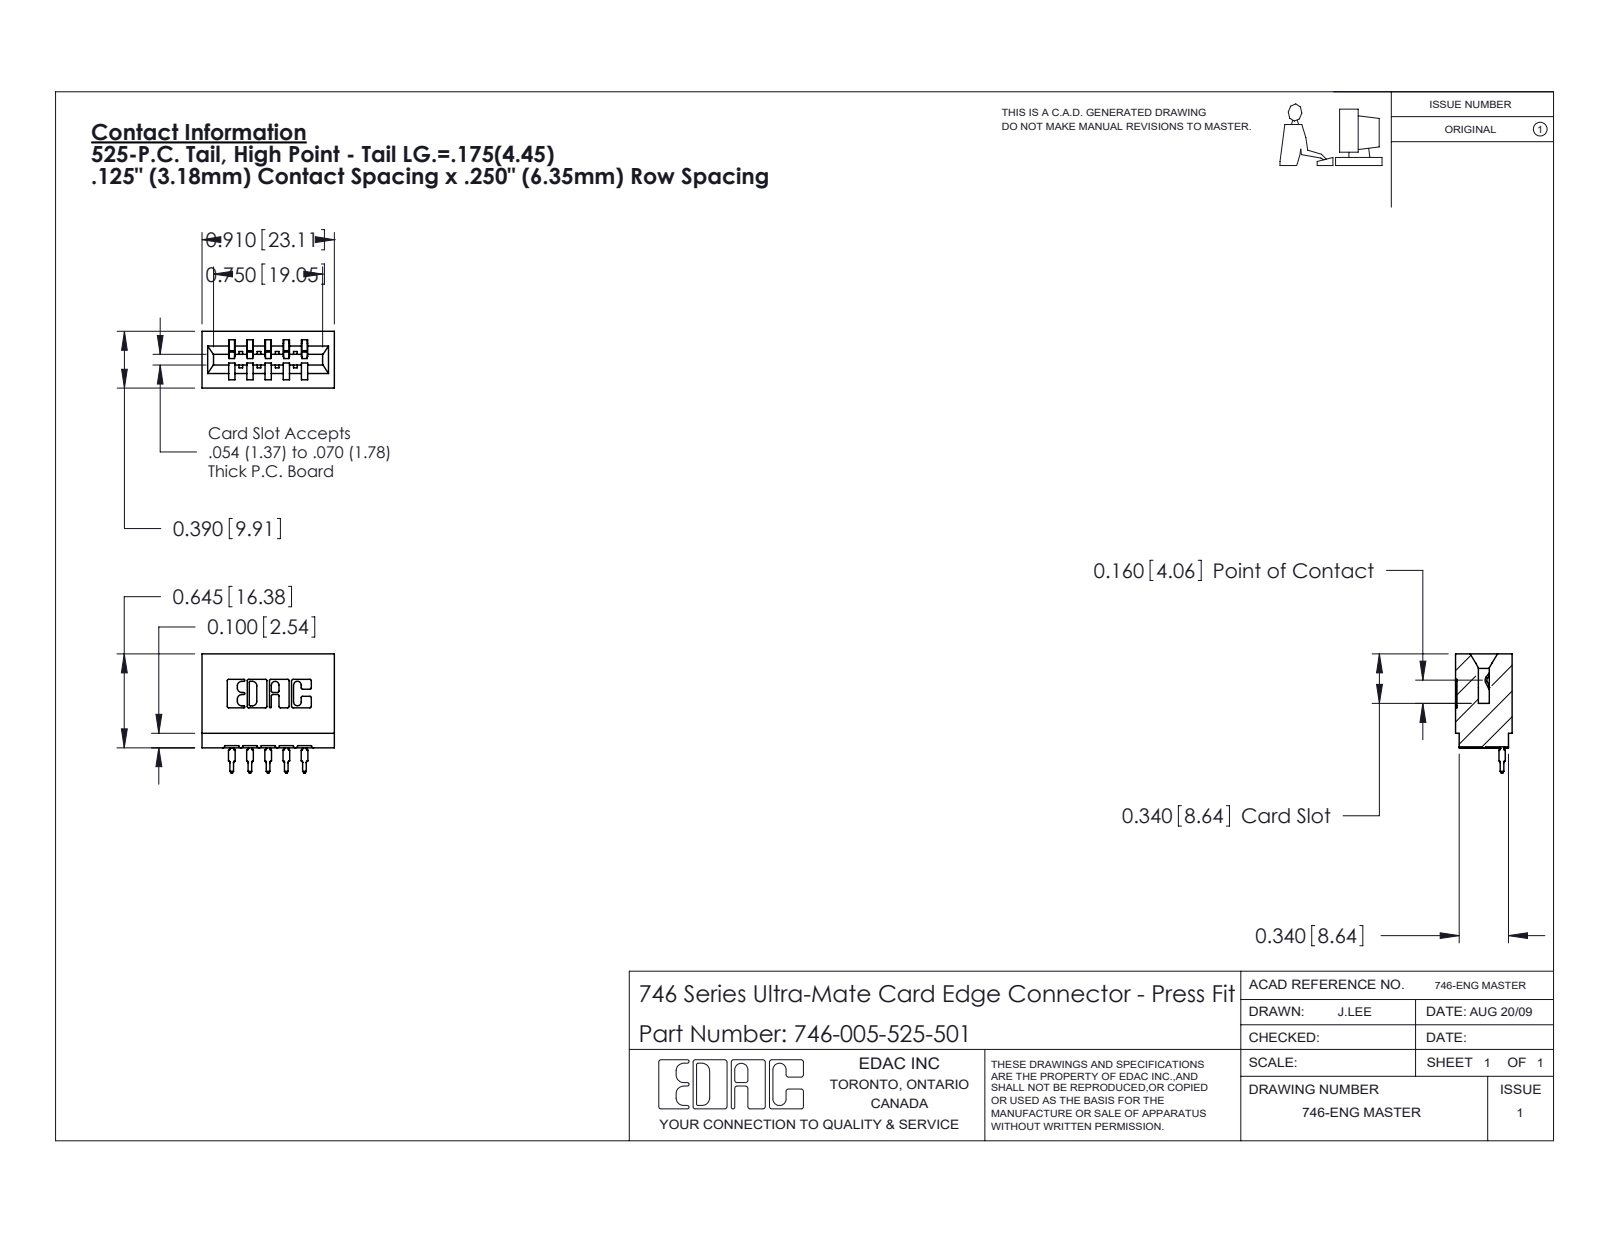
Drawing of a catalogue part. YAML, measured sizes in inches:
part_name: "746-292-001_525; 746-005-525-501; 746 Part_.340 Slot Depth - 01"
step_written_by: "SolidWorks 2020 (CONFIG_CONTROL_DESIGN)"
units: inches
bodies: {solids: 6, faces: 637, planar: 370, cylindrical: 137, other: 130}
overall_size: [0.91, 0.819, 0.39]
volume: 0.172
surface_area: 4.969
partial_cylinders:
  - {radius: 0.01, count: 22}
  - {radius: 0.021, count: 10}
  - {radius: 0.007, count: 6}
  - {radius: 0.015, count: 6}
  - {radius: 0.031, count: 6}
  - {radius: 0.005, count: 4}
  - {radius: 0.011, count: 4}
  - {radius: 0.026, count: 3}
face_to_face_distances: [0.25, 0.042, 0.125, 0.125, 0.333, 0.057, 0.39, 0.292, 0.208, 0.083]
